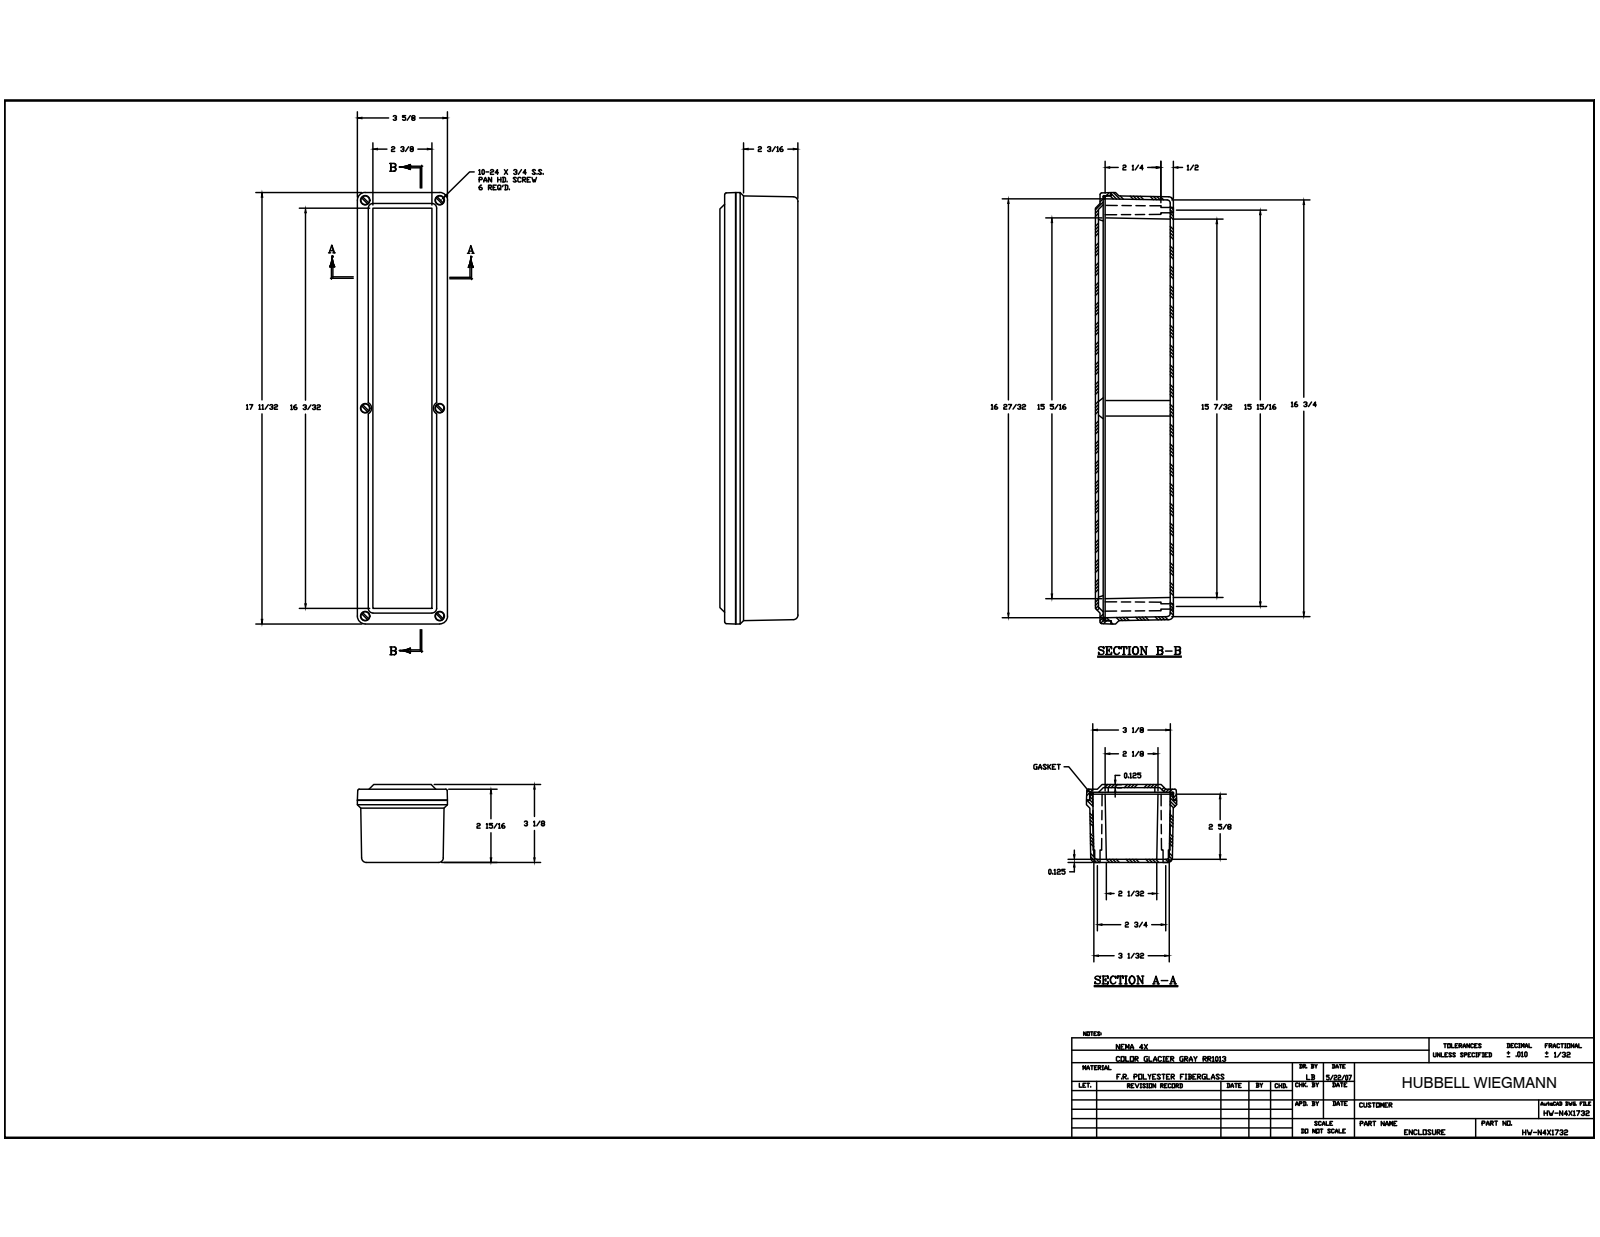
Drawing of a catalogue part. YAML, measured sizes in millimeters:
part_name: "WPCF1732 BOX; 10-24 X 0.4375 DP BRASS INSERT; WPCF1732 CVR; WPCF1732 GASKET (+3 more)"
step_written_by: "Autodesk Inventor 2014 (AUTOMOTIVE_DESIGN)"
units: millimeters
bodies: {solids: 15, faces: 503, planar: 225, cylindrical: 148, other: 130}
overall_size: [440.6, 92.08, 79.38]
volume: 573954
surface_area: 339857
round_holes:
  - {diameter: 5.56, count: 8}
  - {diameter: 3.68, count: 6}
  - {diameter: 4.83, count: 6}
  - {diameter: 9.52, count: 6}
  - {diameter: 5.5, count: 2}
round_bosses_or_shafts:
  - {diameter: 9.42, count: 6}
  - {diameter: 5.54, count: 6}
  - {diameter: 4.5, count: 6}
  - {diameter: 11.18, count: 2}
partial_cylinders:
  - {radius: 0.3, count: 24}
  - {radius: 0.79, count: 20}
  - {radius: 1.22, count: 8}
  - {radius: 1.59, count: 4}
  - {radius: 4.47, count: 4}
  - {radius: 4.76, count: 4}
  - {radius: 5.59, count: 4}
  - {radius: 7.94, count: 4}
face_to_face_distances: [3.18, 3.09, 76.2, 79.38, 73.02, 3.17, 7.94, 4.76, 1.59, 68.26]
hole_center_spacings: [10.45, 73.69, 202.43, 212.36, 215.18, 225.62, 414.78, 421.15]
